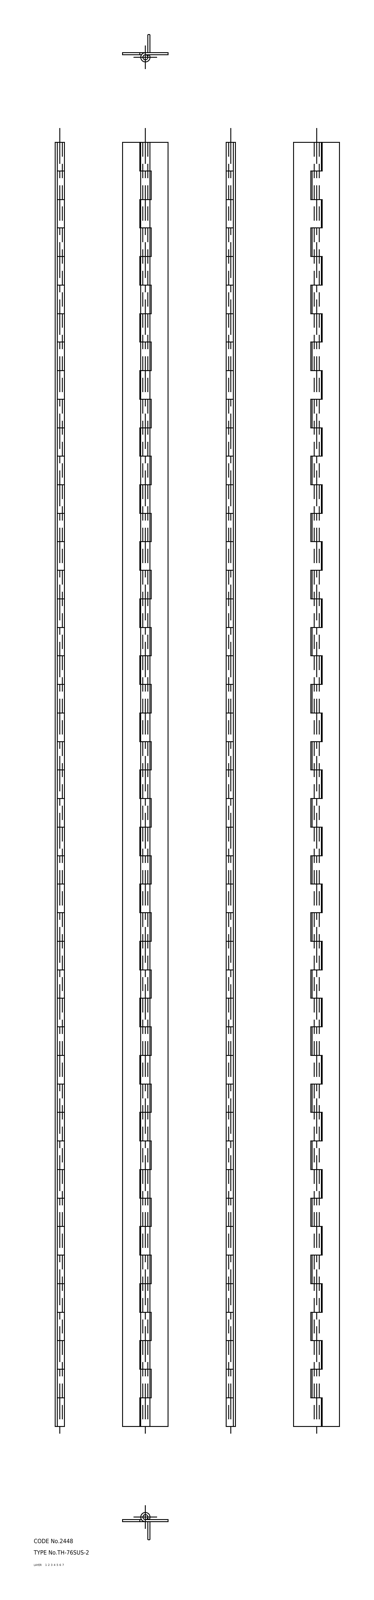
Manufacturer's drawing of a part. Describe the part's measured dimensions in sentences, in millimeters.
The part is named "shaft; hinge piece_B; hinge piece_A; TH_76SUS_2_15387_36". Its 3-D file was written by "CADfix (AUTOMOTIVE_DESIGN)". It is 3 solids with 282 faces: 0 planar, 0 cylindrical and 282 other. Overall it measures 900 by 32 by 6.5 millimeters. Its volume is 64 238 cubic millimeters and its surface area 91 797 square millimeters.
